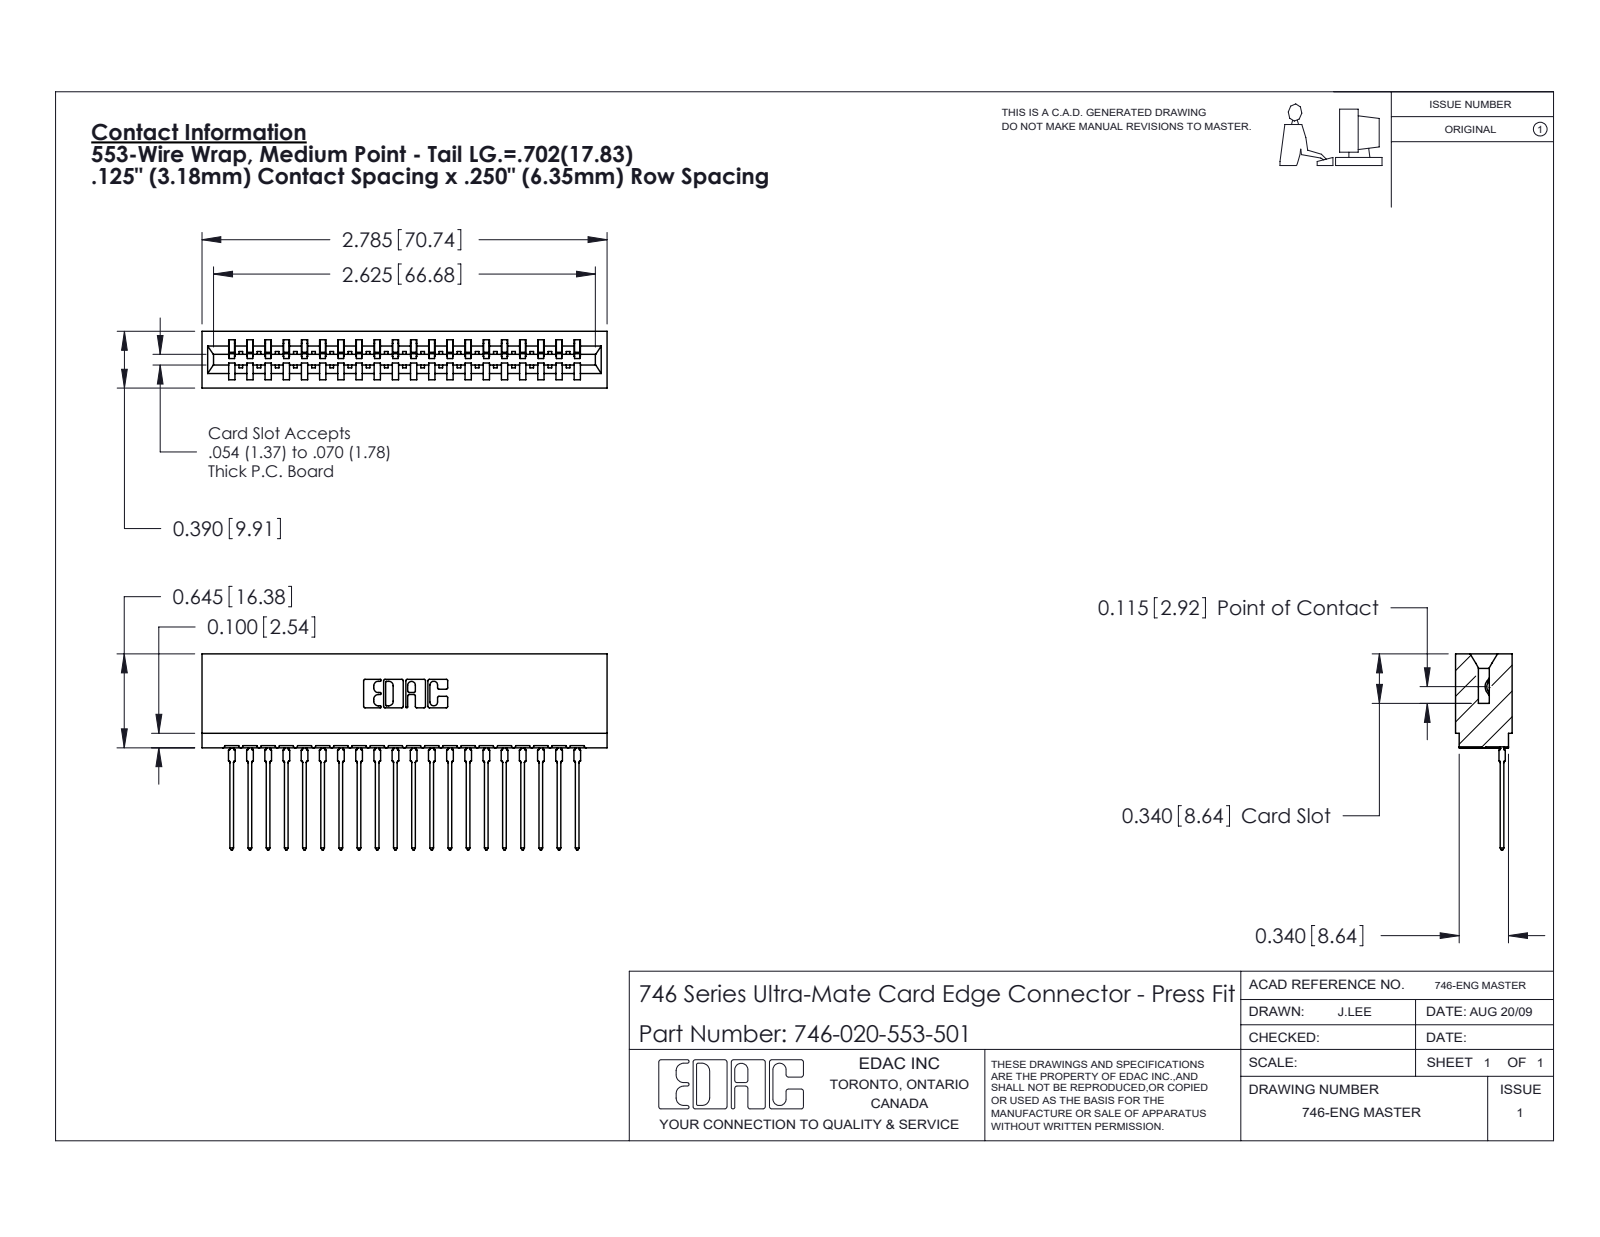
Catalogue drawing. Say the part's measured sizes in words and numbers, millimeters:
The part is named "746-292-001_553; 746 Part_.340 Slot Depth - 01; 746-020-553-501". Its 3-D file was written by "SolidWorks 2020 (CONFIG_CONTROL_DESIGN)". It is 21 solids with 2257 faces: 1315 planar, 422 cylindrical and 520 other. Overall it measures 70.7 by 34.2 by 9.9 millimeters. Its volume is 8 160 cubic millimeters and its surface area 11 040 square millimeters. Partial cylindrical surfaces (rounded edges, fillets, slot ends): 40 of radius 0.5, 22 of radius 0.3, 21 of radius 0.4, 6 of radius 0.2, 6 of radius 0.8, 4 of radius 0.1, 4 of radius 0.3, 3 of radius 0.7. The main face-to-face distances are 6.4, 1.4, 8.5, 9.9, 12.7, 0.6, 7.8, 3.2, 7.4, 3.2.
